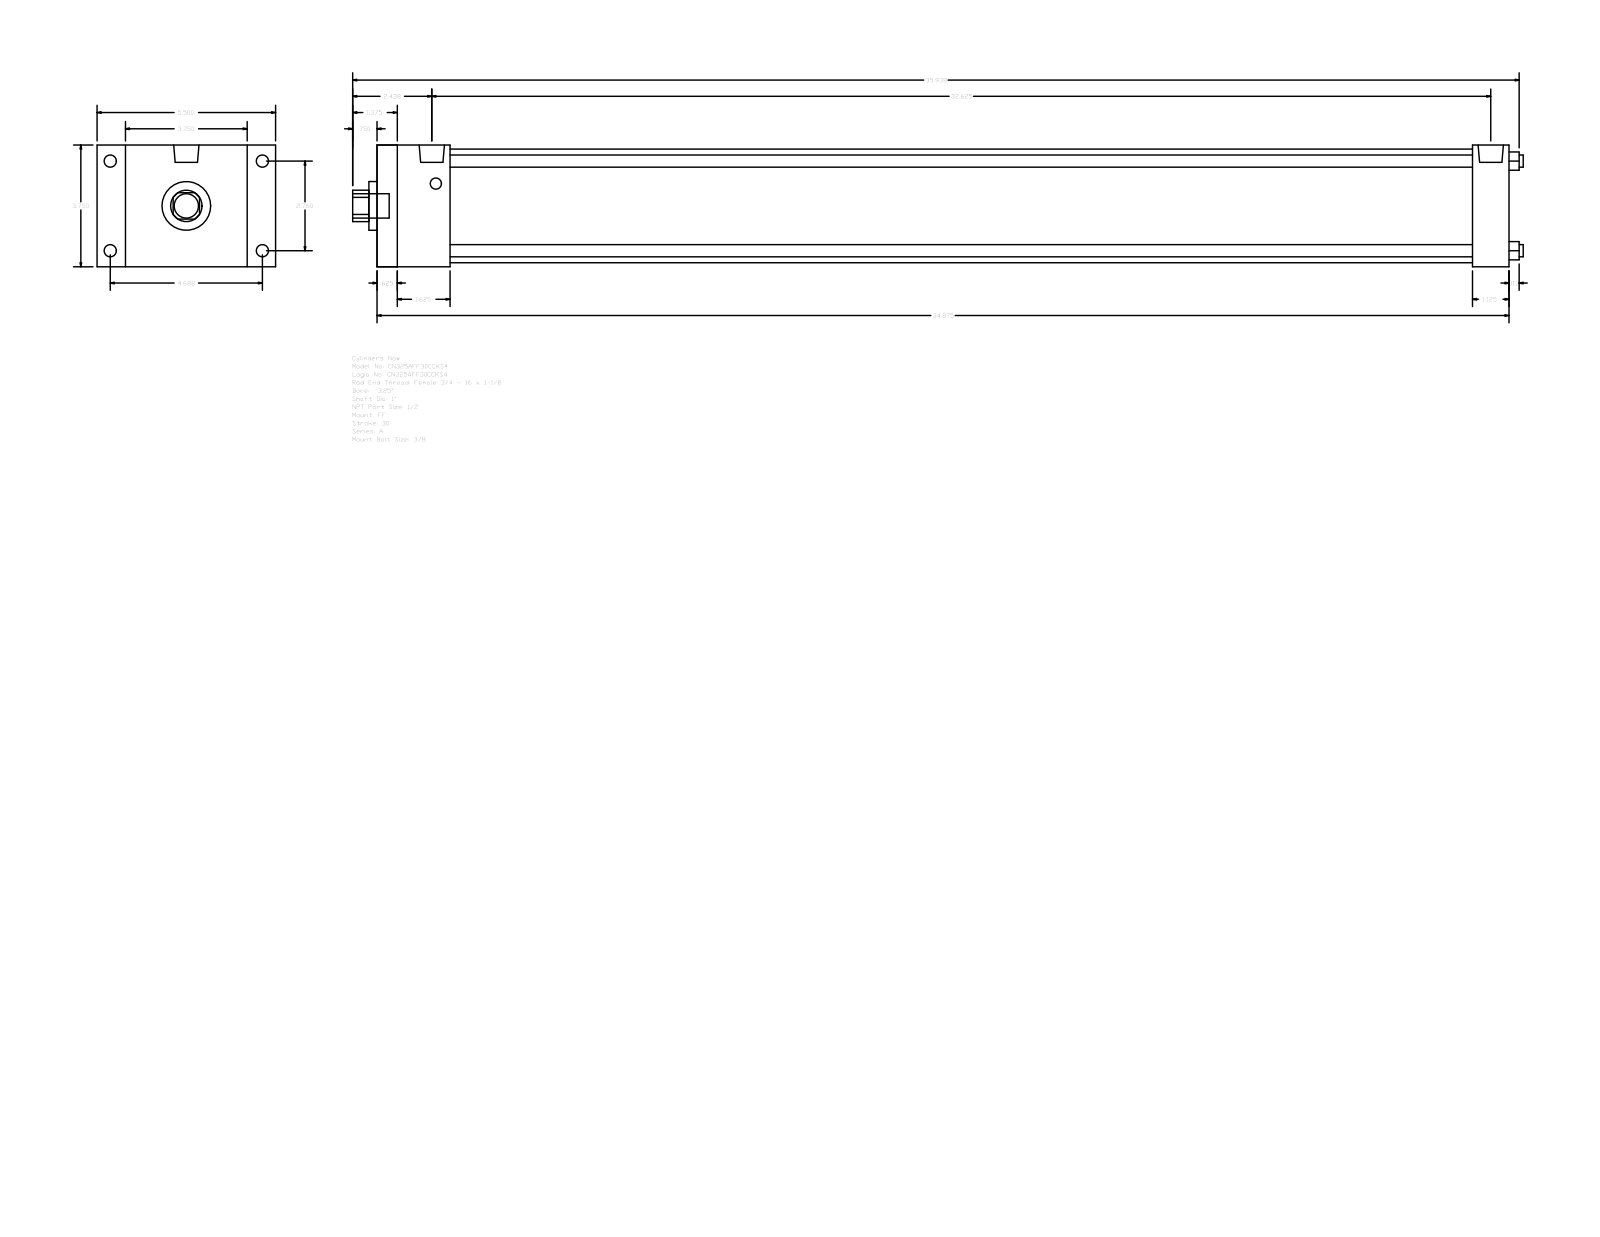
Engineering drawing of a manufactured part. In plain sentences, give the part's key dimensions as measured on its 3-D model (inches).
The part is named "A_FF__0325_1". Its 3-D file was written by "GSSL Pune (CONFIG_CONTROL_DESIGN)". It is 0 solids with 92 faces: 64 planar, 28 cylindrical and 0 other. Overall it measures 36.063 by 5.5 by 3.75 inches. Round holes: 4 of diameter 0.375, 1 of diameter 1, 1 of diameter 1.5, 1 of diameter 3.5. Round bosses or shafts: 4 of diameter 0.375, 4 of diameter 0.344, 2 of diameter 0.778, 1 of diameter 0.75. Partial cylindrical surfaces (rounded edges, fillets, slot ends): 1 of radius 0.484. The main face-to-face distances are 3.75, 34.875, 0.625, 34.25, 0.875, 4.625, 2.25, 33.75, 1.625, 33.125. The hole center spacings are 1.952, 2.76, 3.903.
